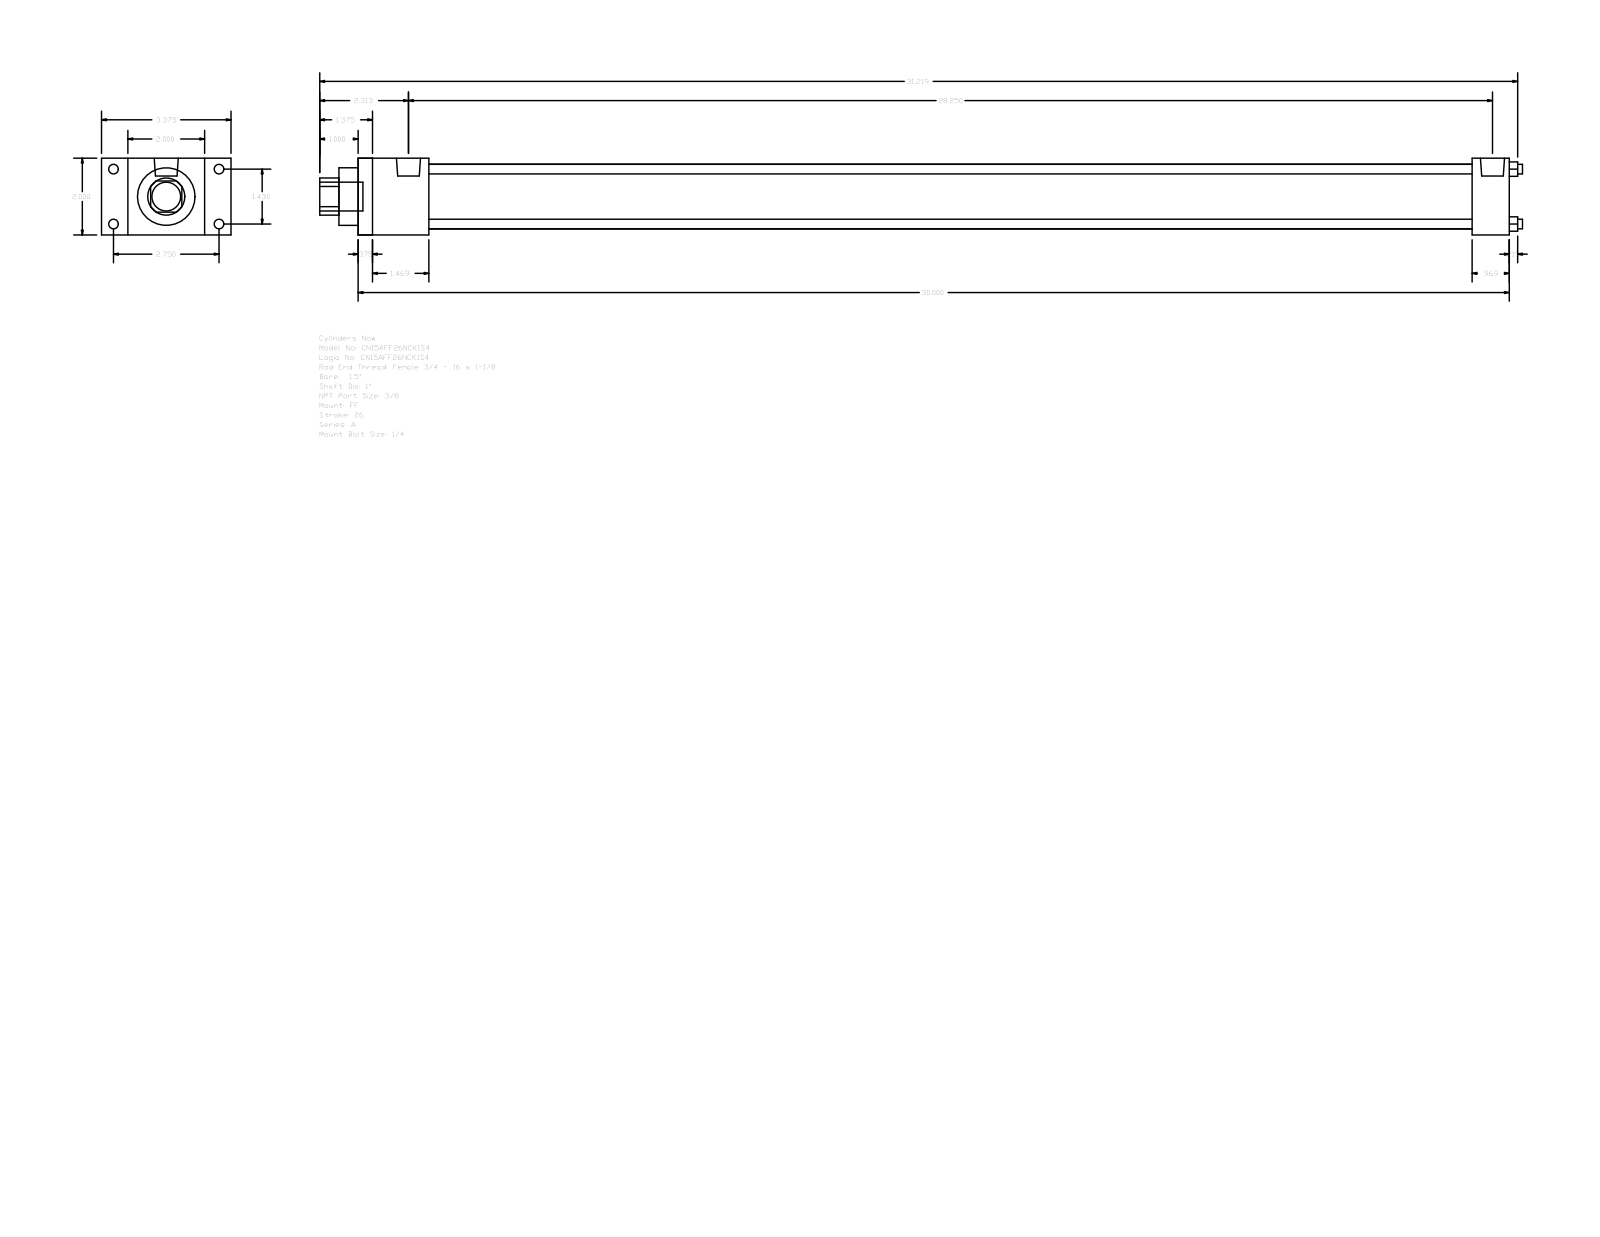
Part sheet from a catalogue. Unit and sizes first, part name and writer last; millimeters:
Units: millimetres
Overall size (bounding box): 796.13 × 85.72 × 50.8
Round holes (diameter × count): ⌀6.35 ×4, ⌀25.4 ×1, ⌀38.1 ×1, ⌀42.93 ×1
Round bosses / shafts (diameter × count): ⌀6.35 ×4, ⌀5.56 ×4, ⌀15.93 ×2, ⌀19.05 ×1
Partial cylindrical surfaces — rounded edges, fillets, slot ends (radius × count): R12.29 ×1
Main face-to-face distances: 50.8, 762, 9.52, 752.48, 46.83, 737.39, 37.31, 727.87, 690.56, 715.17
Hole centre spacings: 25.68, 36.32, 51.36
Bodies: 0 solids, 92 faces (64 planar, 28 cylindrical, 0 other)
Part name (STEP PRODUCT): A_FF__0150_1
STEP written by: GSSL Pune (CONFIG_CONTROL_DESIGN)
